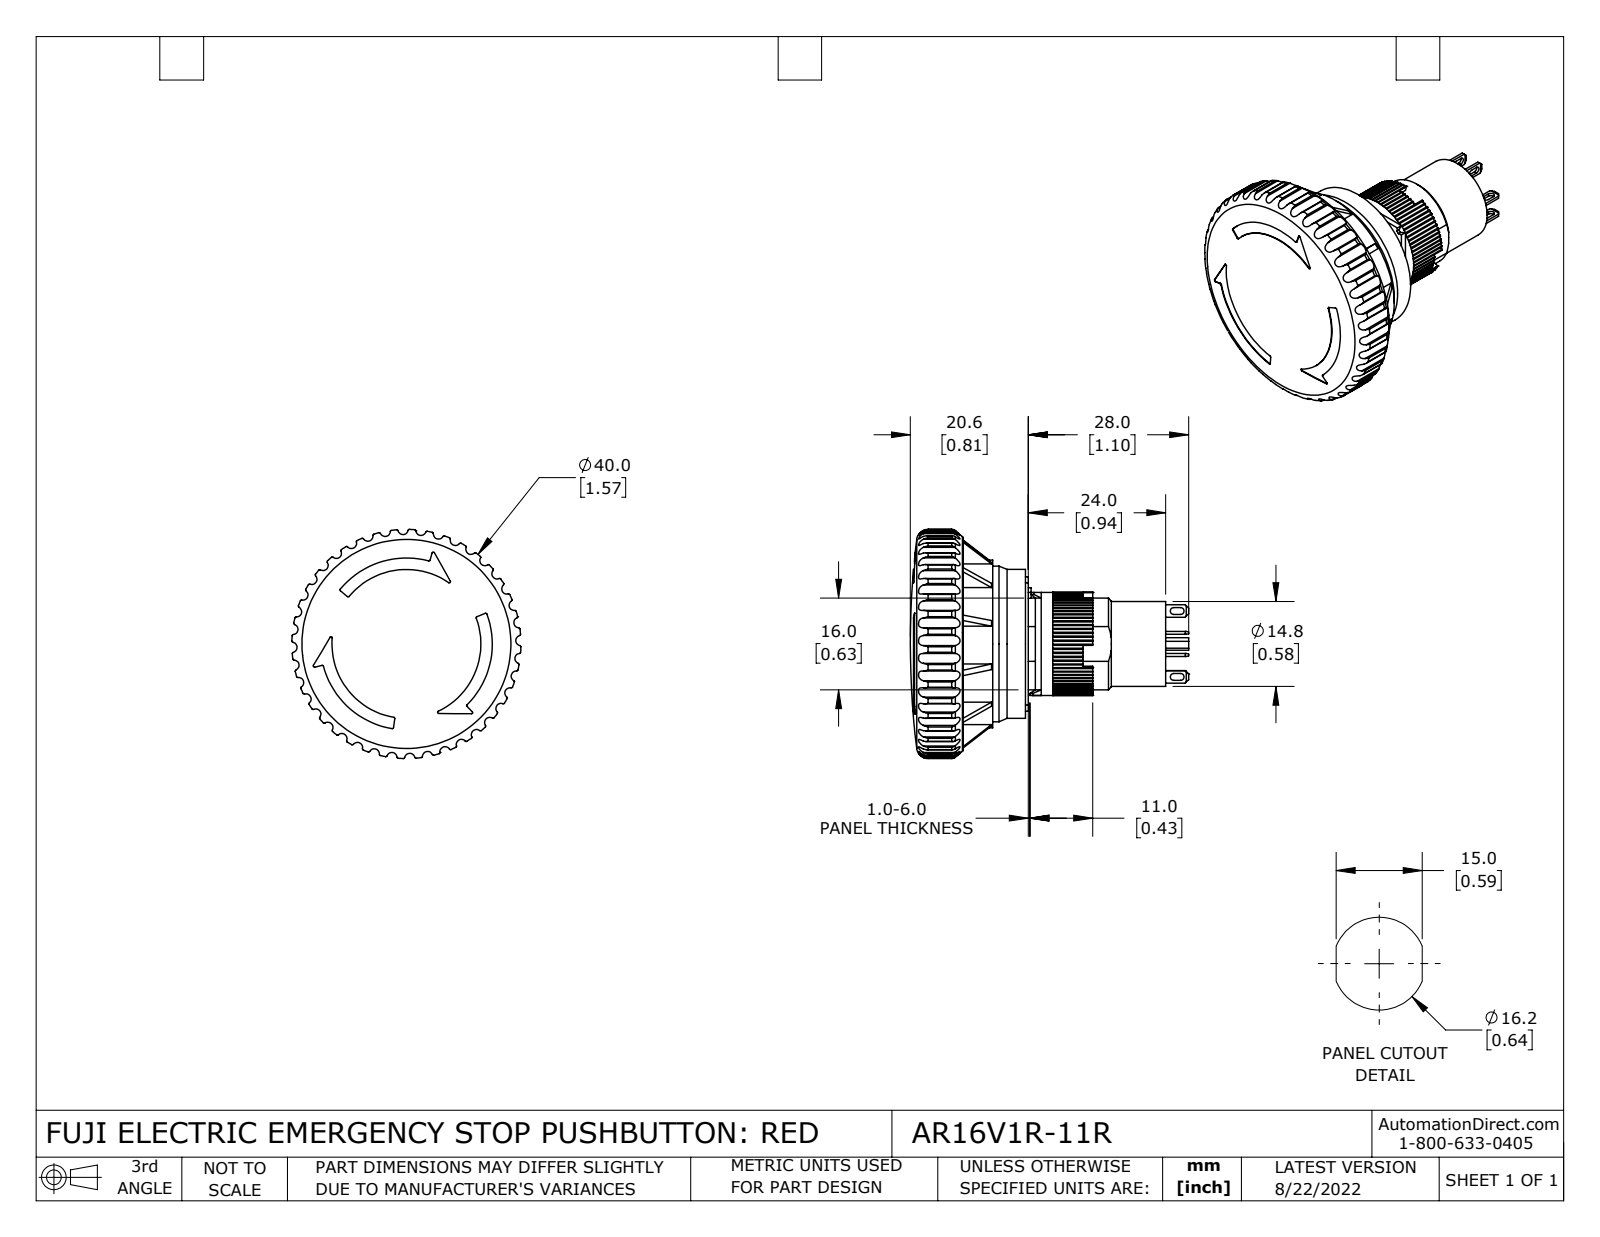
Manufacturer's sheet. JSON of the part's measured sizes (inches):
{"part_name": "AR16V1R-11R", "step_written_by": "SolidWorks 2021 (CONFIG_CONTROL_DESIGN)", "units": "inches", "bodies": {"solids": 5, "faces": 1001, "planar": 495, "cylindrical": 410, "other": 96}, "overall_size": [1.913, 1.575, 1.575], "volume_in3": 0.963, "surface_area_in2": 19.04, "round_holes": [[0.583, 1], [0.63, 1], [0.709, 1], [1.069, 1], [1.433, 1]], "round_bosses_or_shafts": [[1.154, 1], [1.024, 1], [0.858, 1], [0.236, 1]], "partial_cylinders_radius": [[0.008, 80], [0.01, 80], [0.035, 40], [0.02, 8], [0.024, 8], [0.039, 2], [0.031, 1], [0.114, 1]], "face_to_face_distances": [0.039, 0.421, 0.53, 0.108, 0.02, 0.069, 0.856, 0.49, 0.089, 0.049]}
